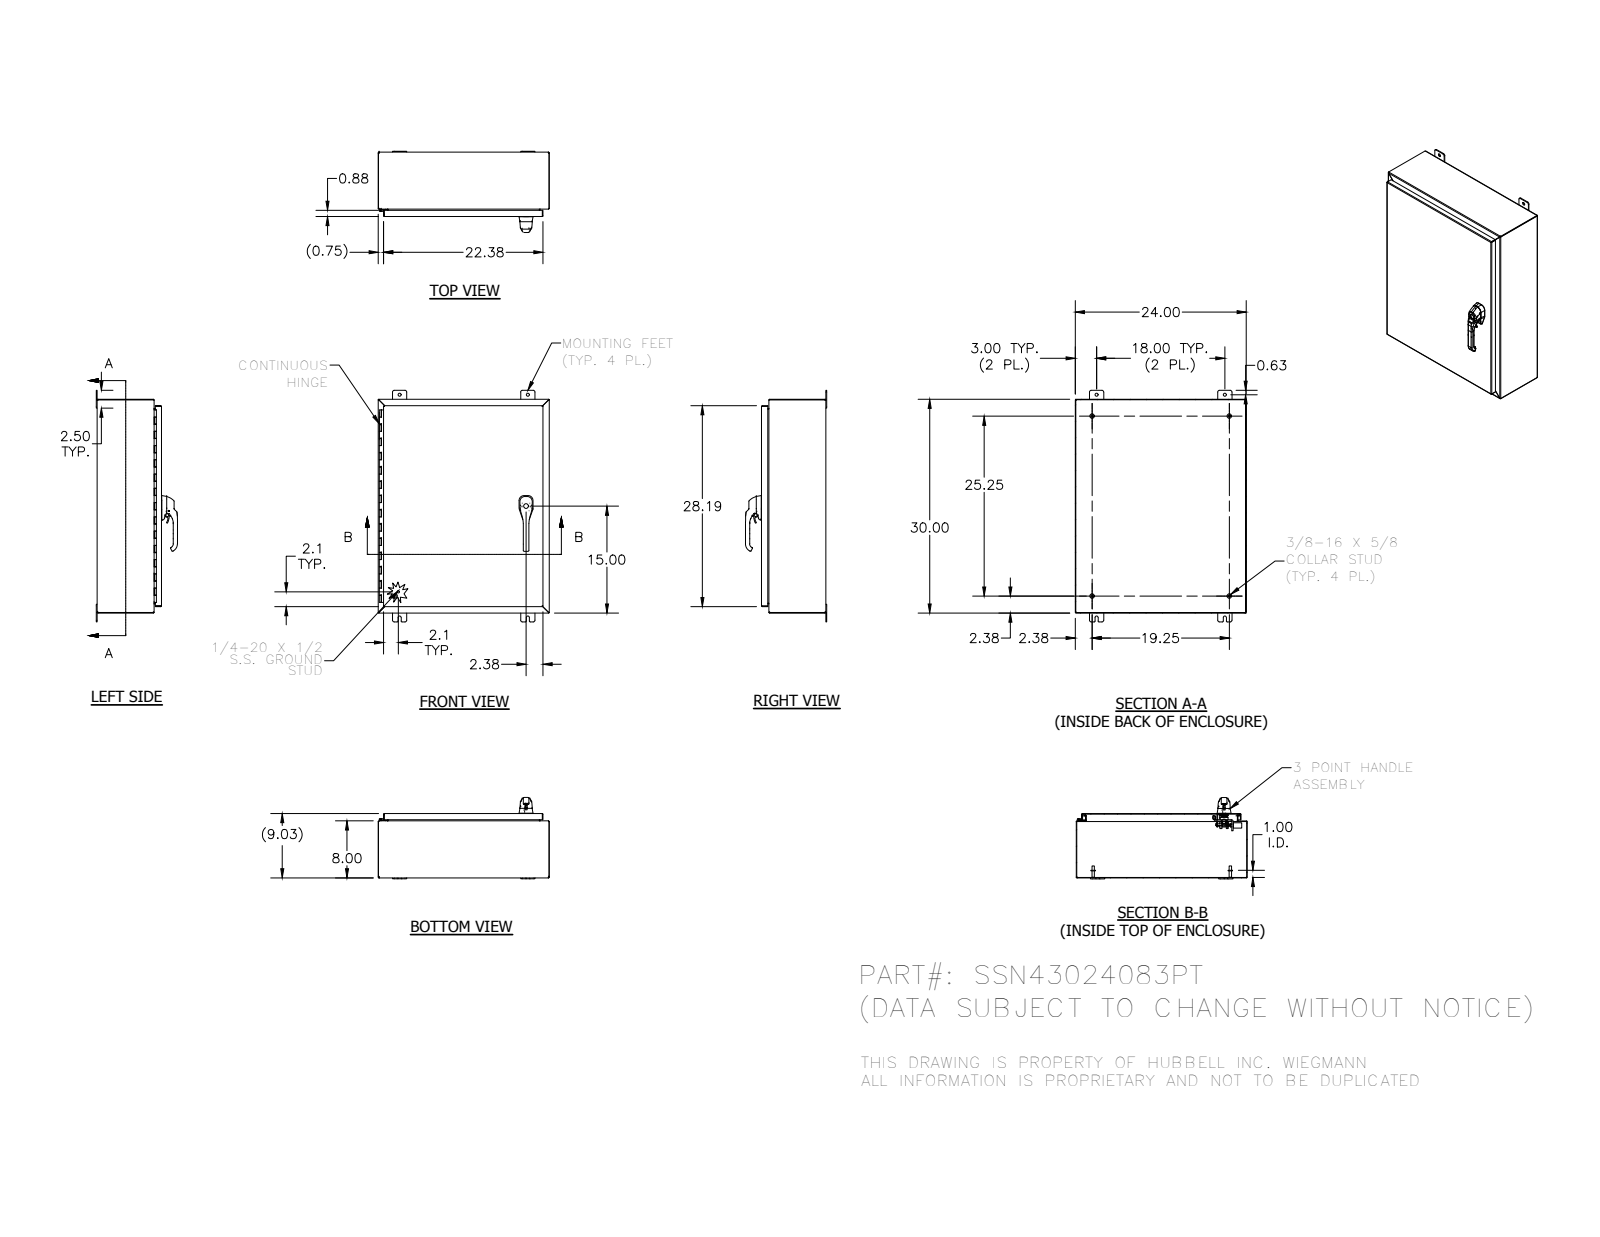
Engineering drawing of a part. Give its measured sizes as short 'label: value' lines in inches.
name: SSN43024083PTBKP; 1000-277-01; PLASTIC-ROLLER-CAM_AF1; 34871 (+8 more)
written by: SolidWorks 2014 (AUTOMOTIVE_DESIGN)
unit: in
bodies: 56 solids, 3128 faces (1047 planar, 1296 cylindrical, 785 other)
size: 32.5 × 24 × 11.408
volume: 217.2 in³; area: 5 615 in²
holes: 8× ⌀0.262, 4× ⌀0.187, 4× ⌀0.438, 3× ⌀0.213, 3× ⌀0.281, 2× ⌀0.241, 2× ⌀0.25, 2× ⌀0.252, 2× ⌀0.315, 2× ⌀0.4, 2× ⌀0.402, 2× ⌀0.413
bosses: 4× ⌀0.625, 4× ⌀0.33, 3× ⌀0.236, 2× ⌀1, 2× ⌀0.563, 2× ⌀0.533, 2× ⌀0.531, 2× ⌀0.5
rounds: 172× R0.02, 113× R0.012, 26× R0.125, 24× R0.031, 21× R0.019, 20× R0.105, 20× R0.25, 16× R0.025
face distances: 0.074, 8.959, 8.885, 9.033, 23.926, 29.926, 7.926, 1.033, 24, 23.852
hole spacings: 0.38, 0.492, 0.76, 0.886, 20.428, 0.234, 0.258, 0.38
